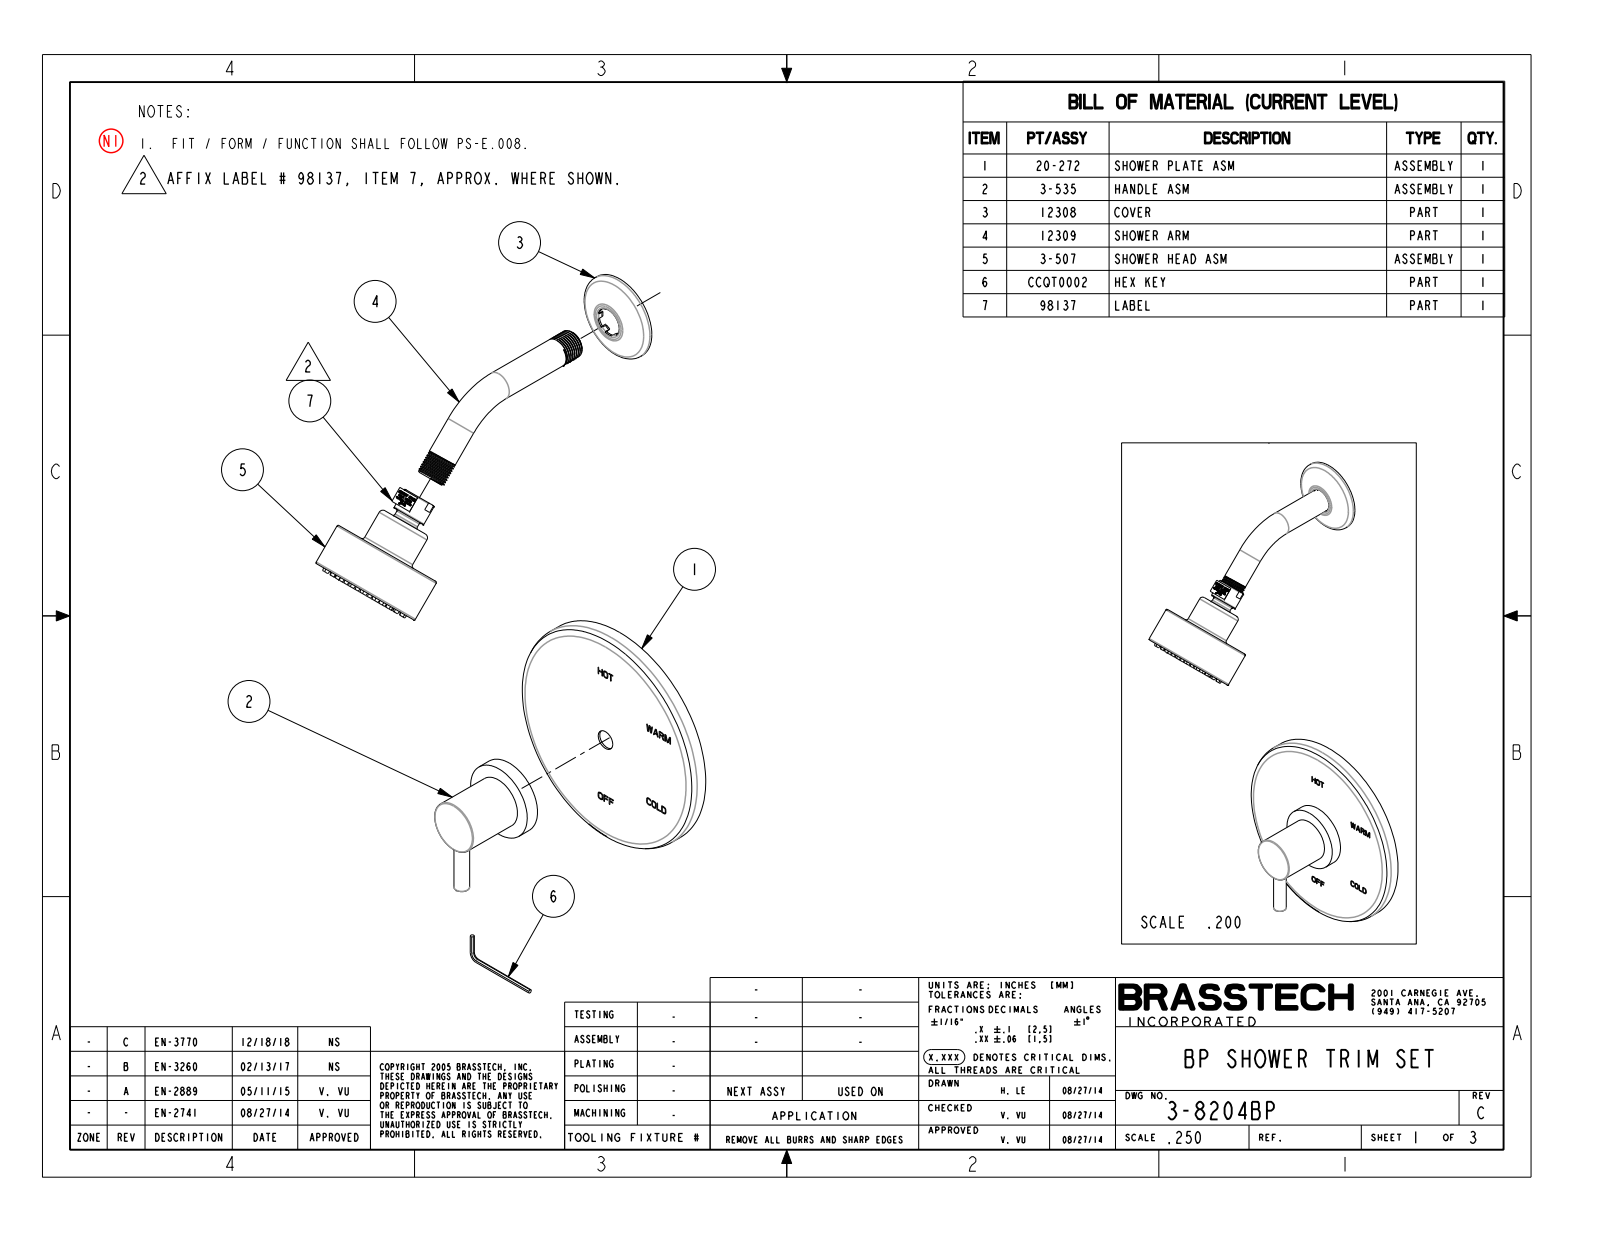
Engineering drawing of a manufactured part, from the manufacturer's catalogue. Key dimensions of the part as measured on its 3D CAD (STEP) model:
Part name (STEP PRODUCT): NCIP-025_AF0; CTWR_1; 2-965_AF0_ASM; NCIP-024-2_1 (+8 more)
STEP written by: PRO/ENGINEER BY PARAMETRIC TECHNOLOGY CORPORATION, 2013150 (CONFIG_CONTROL_DESIGN)
Units: inches
Bodies: 14 solids, 1368 faces (629 planar, 411 cylindrical, 328 other)
Overall size (bounding box): 18.596 × 7.942 × 6.693
Volume: 18.39 in³ · Surface area: 293.6 in²
Round holes (diameter × count): ⌀0.039 ×48, ⌀0.315 ×2, ⌀0.685 ×2, ⌀0.156 ×1, ⌀0.165 ×1, ⌀0.256 ×1, ⌀0.335 ×1, ⌀0.465 ×1, ⌀0.492 ×1, ⌀0.531 ×1, ⌀0.563 ×1, ⌀0.579 ×1
Round bosses / shafts (diameter × count): ⌀0.811 ×2, ⌀0.236 ×2, ⌀6.693 ×1, ⌀6.593 ×1, ⌀3.15 ×1, ⌀2.5 ×1, ⌀2.2 ×1, ⌀1.969 ×1
Partial cylindrical surfaces — rounded edges, fillets, slot ends (radius × count): R0.004 ×30, R0.03 ×20, R0.015 ×15, R0.016 ×6, R0.039 ×5, R0.059 ×5, R0.016 ×2, R0.079 ×1
Main face-to-face distances: 0.059, 0.354, 0.413, 1.22, 0.4, 0.34, 0.459, 0.813, 0.551, 0.138
Hole centre spacings: 0.752, 1.003, 1.967, 1.002, 1.418, 1.453, 1.667, 0.389
